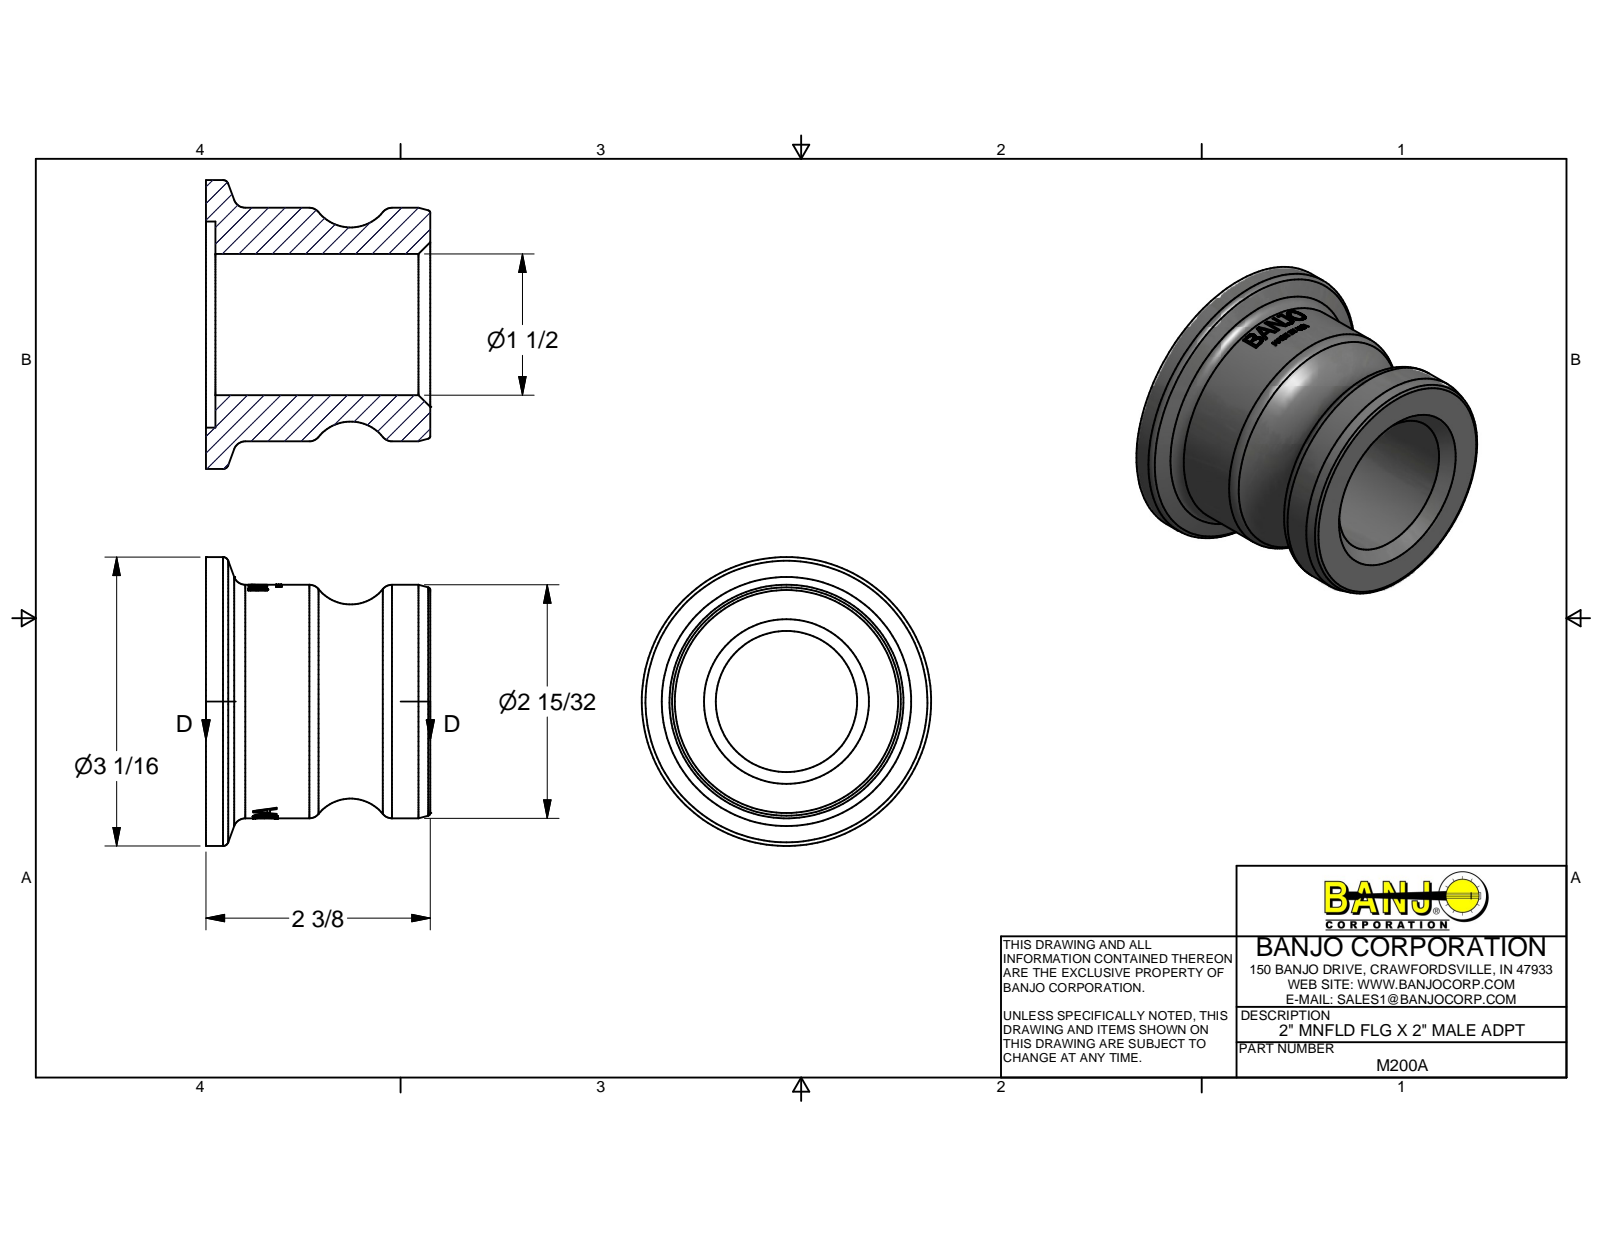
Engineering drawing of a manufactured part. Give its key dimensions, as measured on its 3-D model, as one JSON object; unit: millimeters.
{"part_name": "M200A", "step_written_by": "Autodesk Inventor 2013 (AUTOMOTIVE_DESIGN)", "units": "millimeters", "bodies": {"solids": 1, "faces": 300, "planar": 156, "cylindrical": 35, "other": 109}, "overall_size": [78, 78, 60.5], "volume_mm3": 113900, "surface_area_mm2": 26120, "round_holes": [[38.1, 1], [55.6, 1]], "round_bosses_or_shafts": [[78, 1], [63, 1]], "partial_cylinders_radius": [[31.3, 1]], "face_to_face_distances": [60.5, 2.5, 57.9, 16.5, 8.9, 3.8, 0.6, 3, 19.1, 41.4]}
